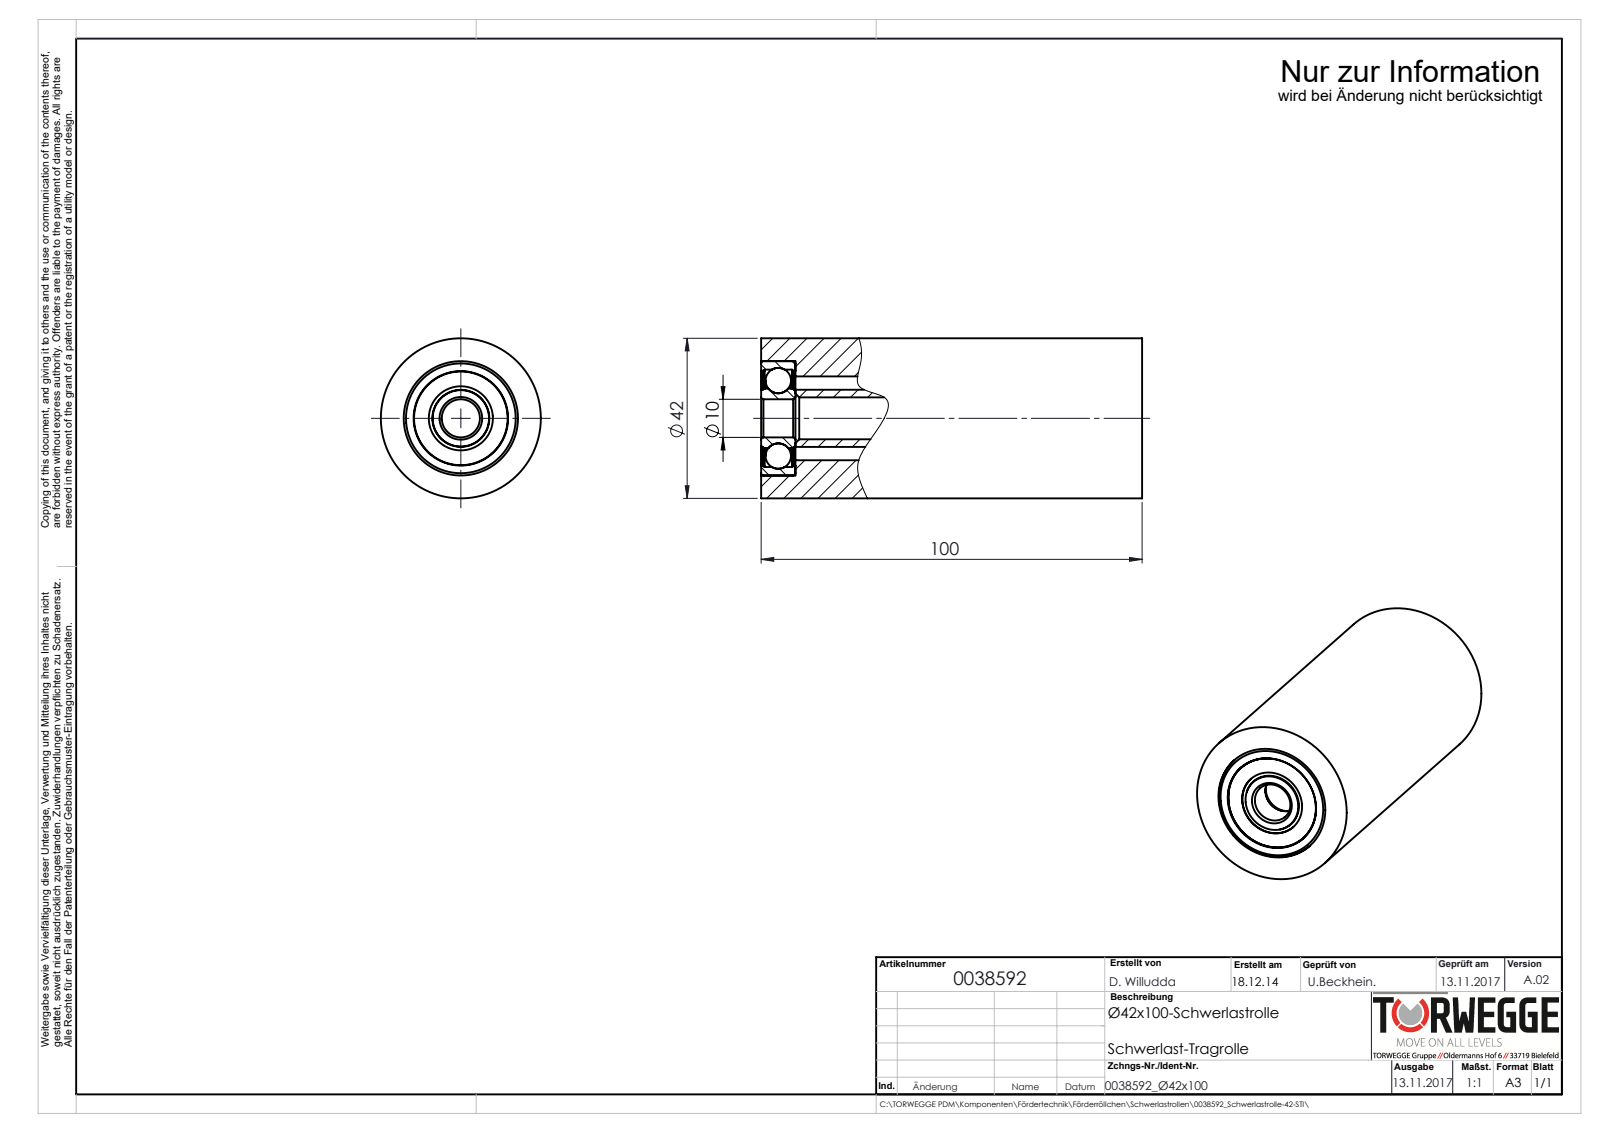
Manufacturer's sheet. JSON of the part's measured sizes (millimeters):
{"part_name": "0038304_003-Distanzrohr-Ø15x2x86; 0038592_001-Rohr42-STI; Rillenkugellager_DIN625-6200-2RS; 0038592_Ø42x100-Schwerlastrolle", "step_written_by": "SolidWorks 2016 (AUTOMOTIVE_DESIGN)", "units": "millimeters", "bodies": {"solids": 12, "faces": 182, "planar": 34, "cylindrical": 76, "other": 72}, "overall_size": [100, 42, 42], "volume_mm3": 110952, "surface_area_mm2": 40638, "round_holes": [[10, 1], [11, 1], [16.83, 1], [22, 1], [22.89, 1], [24.8, 1], [25.56, 1], [30, 1]], "round_bosses_or_shafts": [[42, 1], [24.58, 1], [15.62, 1], [15, 1]], "face_to_face_distances": [91, 9, 8.83, 8.38, 100, 0.45, 8.55, 8.1, 82, 91.28]}
